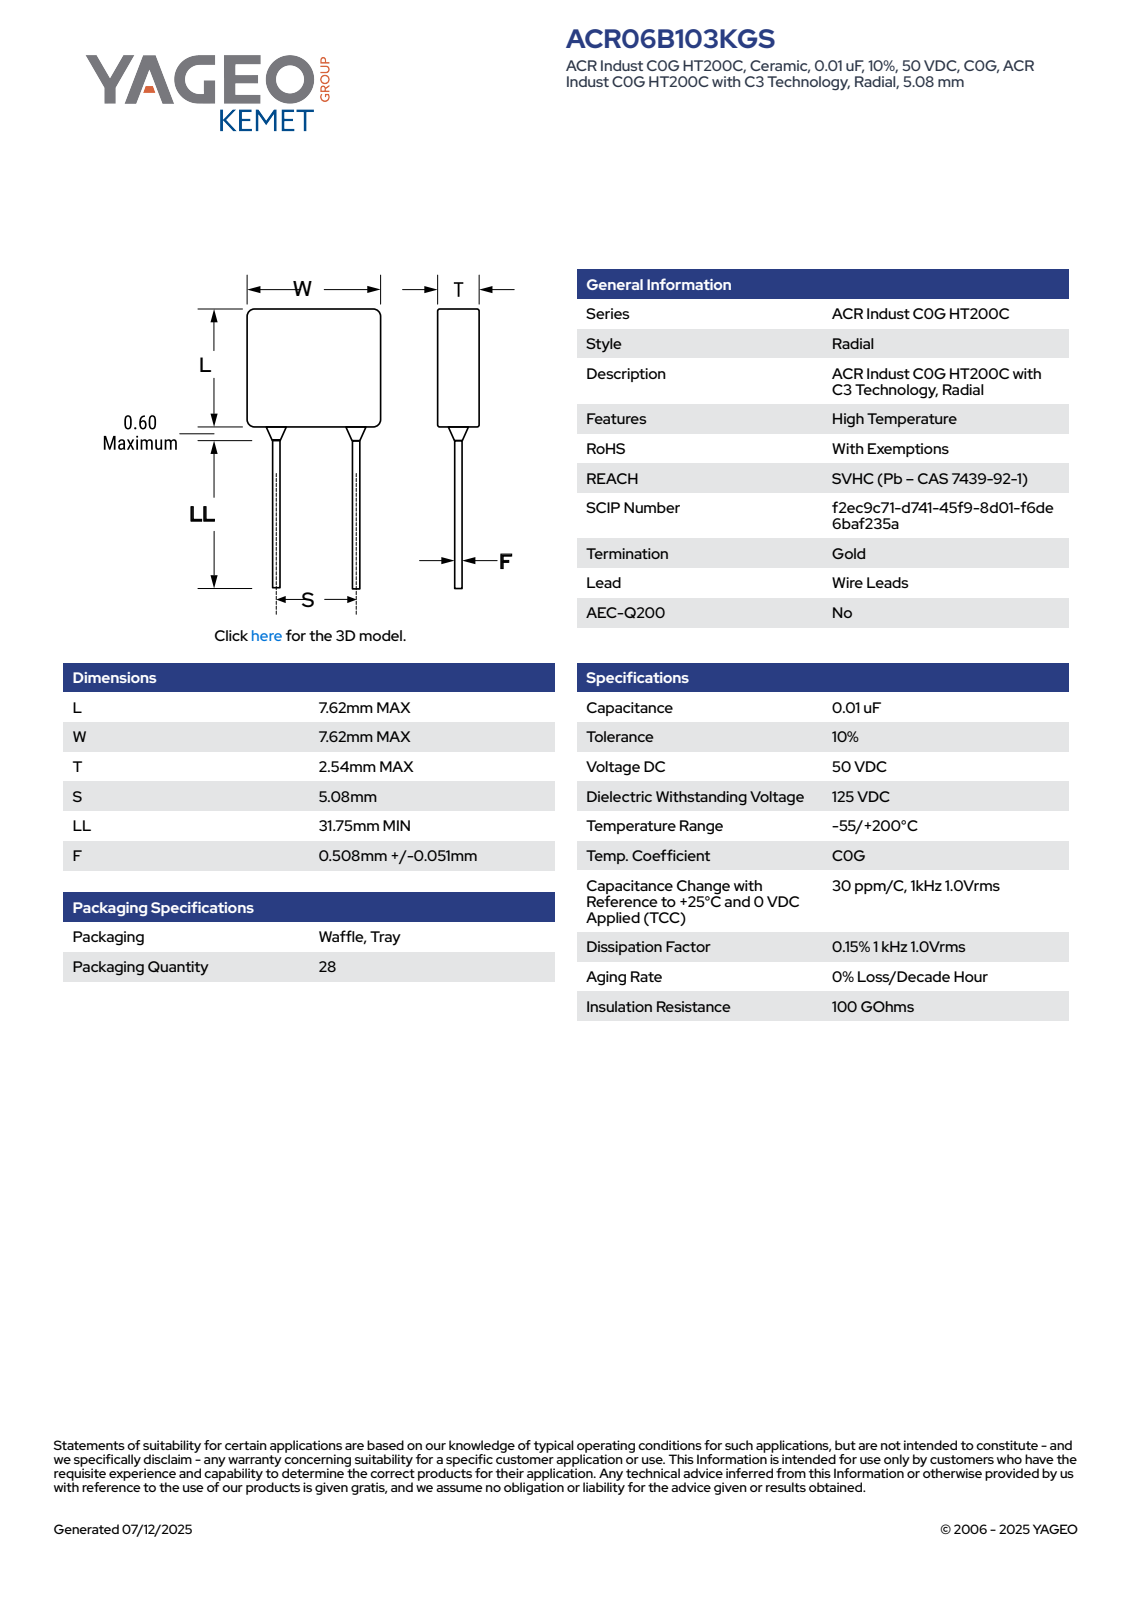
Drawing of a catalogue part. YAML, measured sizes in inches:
part_name: "CCR_C3_6_L7.62T2.54S5.842LL3.175F0.559W7.62"
step_written_by: "SolidWorks 2021 (AUTOMOTIVE_DESIGN)"
units: inches
bodies: {solids: 4, faces: 77, planar: 65, cylindrical: 8, other: 4}
overall_size: [0.434, 0.3, 0.1]
volume: 0.009
surface_area: 0.33
round_bosses_or_shafts:
  - {diameter: 0.022, count: 2}
partial_cylinders:
  - {radius: 0.008, count: 4}
face_to_face_distances: [0.1, 0.3, 0.134, 0.434, 0.304, 0.17, 0.13, 0.258, 0.124, 0.046]
